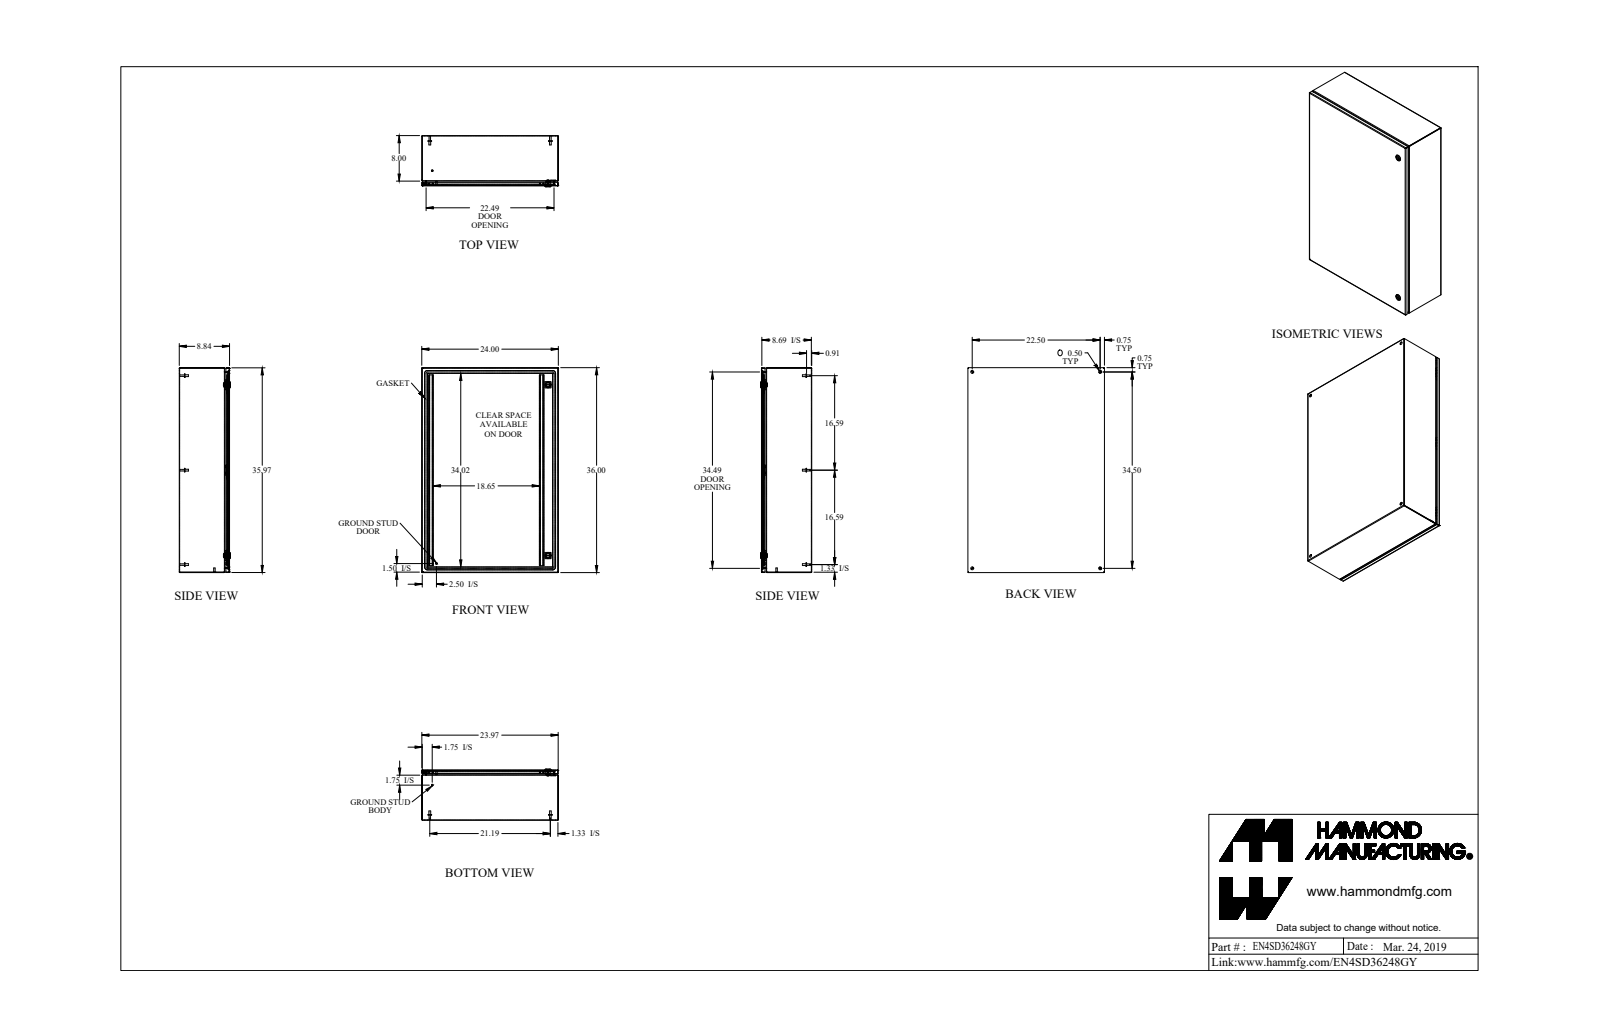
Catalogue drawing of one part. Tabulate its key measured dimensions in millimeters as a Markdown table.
| quantity | value |
| --- | --- |
| part name | EN4SD36248GY_Default |
| STEP written by | SolidWorks 2019 (CONFIG_CONTROL_DESIGN) |
| units | millimeters |
| bodies | 33 solids, 917 faces (430 planar, 307 cylindrical, 180 other) |
| overall size | 914.4 × 609.6 × 228.5 |
| volume | 3 718 000 mm³ |
| surface area | 4 112 000 mm² |
| round holes (diameter × count) | 12.7 × 4, 5.9 × 2, 15.9 × 2, 19.9 × 2, 4.4 × 1, 6.1 × 1, 6.1 × 1 |
| round bosses / shafts (diameter × count) | 15.9 × 6, 8 × 6, 6.9 × 6, 27.9 × 2, 13.3 × 2, 7.1 × 2, 6.4 × 2, 11.6 × 1 |
| partial cylindrical surfaces (radius × count) | 0.9 × 20, 2.7 × 20, 1.1 × 12, 2.1 × 12, 9.7 × 12, 482.7 × 8, 0.2 × 6, 1.6 × 6 |
| main face-to-face distances | 1.8, 222.6, 220.8, 224.5, 607.8, 912.6, 605.9, 609.6, 910.7, 914.4 |
| hole center spacings | 571.5, 876.3, 1046.2, 63.3, 63.3, 547.2, 547.2, 762 |
